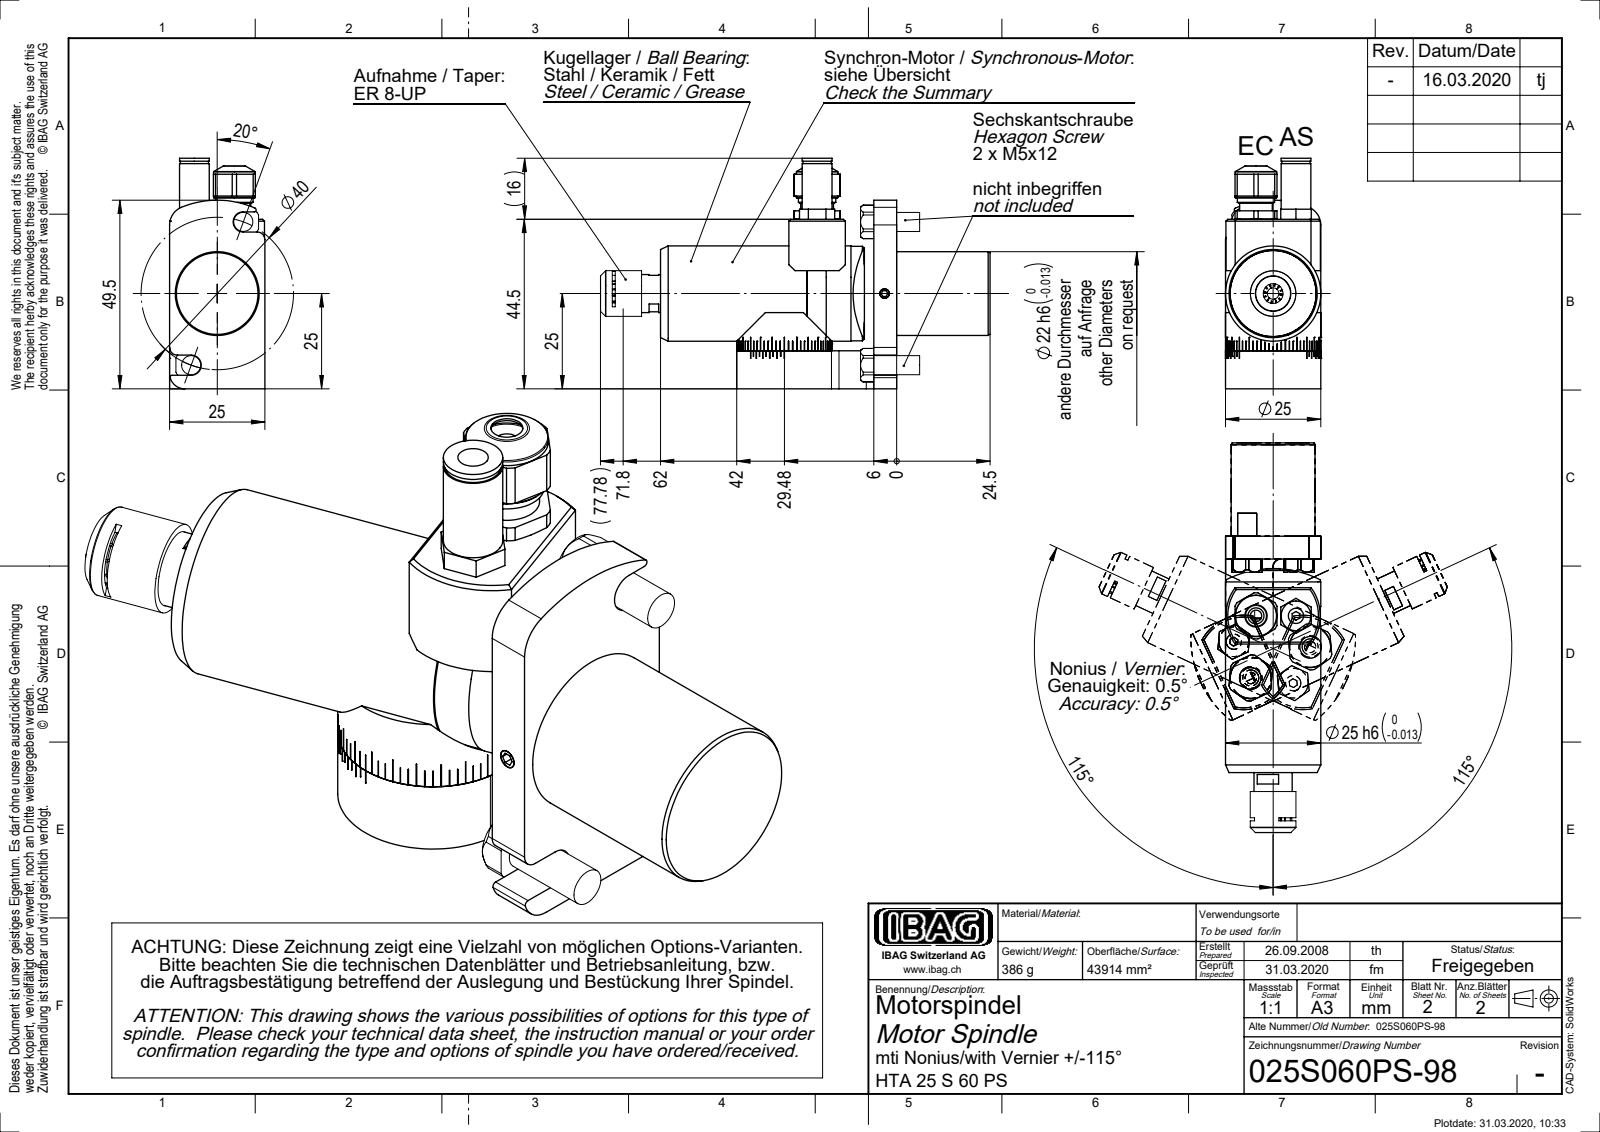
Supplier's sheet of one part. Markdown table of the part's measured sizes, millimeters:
| quantity | value |
| --- | --- |
| part name | 025S060PS-98 |
| STEP written by | SolidWorks 2010 (CONFIG_CONTROL_DESIGN) |
| units | millimeters |
| bodies | 0 solids, 285 faces (131 planar, 119 cylindrical, 35 other) |
| overall size | 102.28 × 60.5 × 25 |
| round holes (diameter × count) | 3 × 2, 2.5 × 1, 4 × 1, 4.2 × 1, 5.2 × 1, 9.15 × 1, 10.6 × 1 |
| round bosses / shafts (diameter × count) | 25 × 2, 5 × 2, 24.8 × 1, 22 × 1, 12 × 1, 10.9 × 1, 10 × 1, 9.79 × 1 |
| partial cylindrical surfaces (radius × count) | 1.55 × 4, 2 × 4, 2.9 × 4, 0.5 × 2, 2.65 × 2, 4.4 × 2, 12.4 × 2, 4 × 1 |
| main face-to-face distances | 6, 10, 5, 24.5, 12, 30.5, 1.8, 56, 62, 86.5 |
| hole center spacings | 10.5 |
